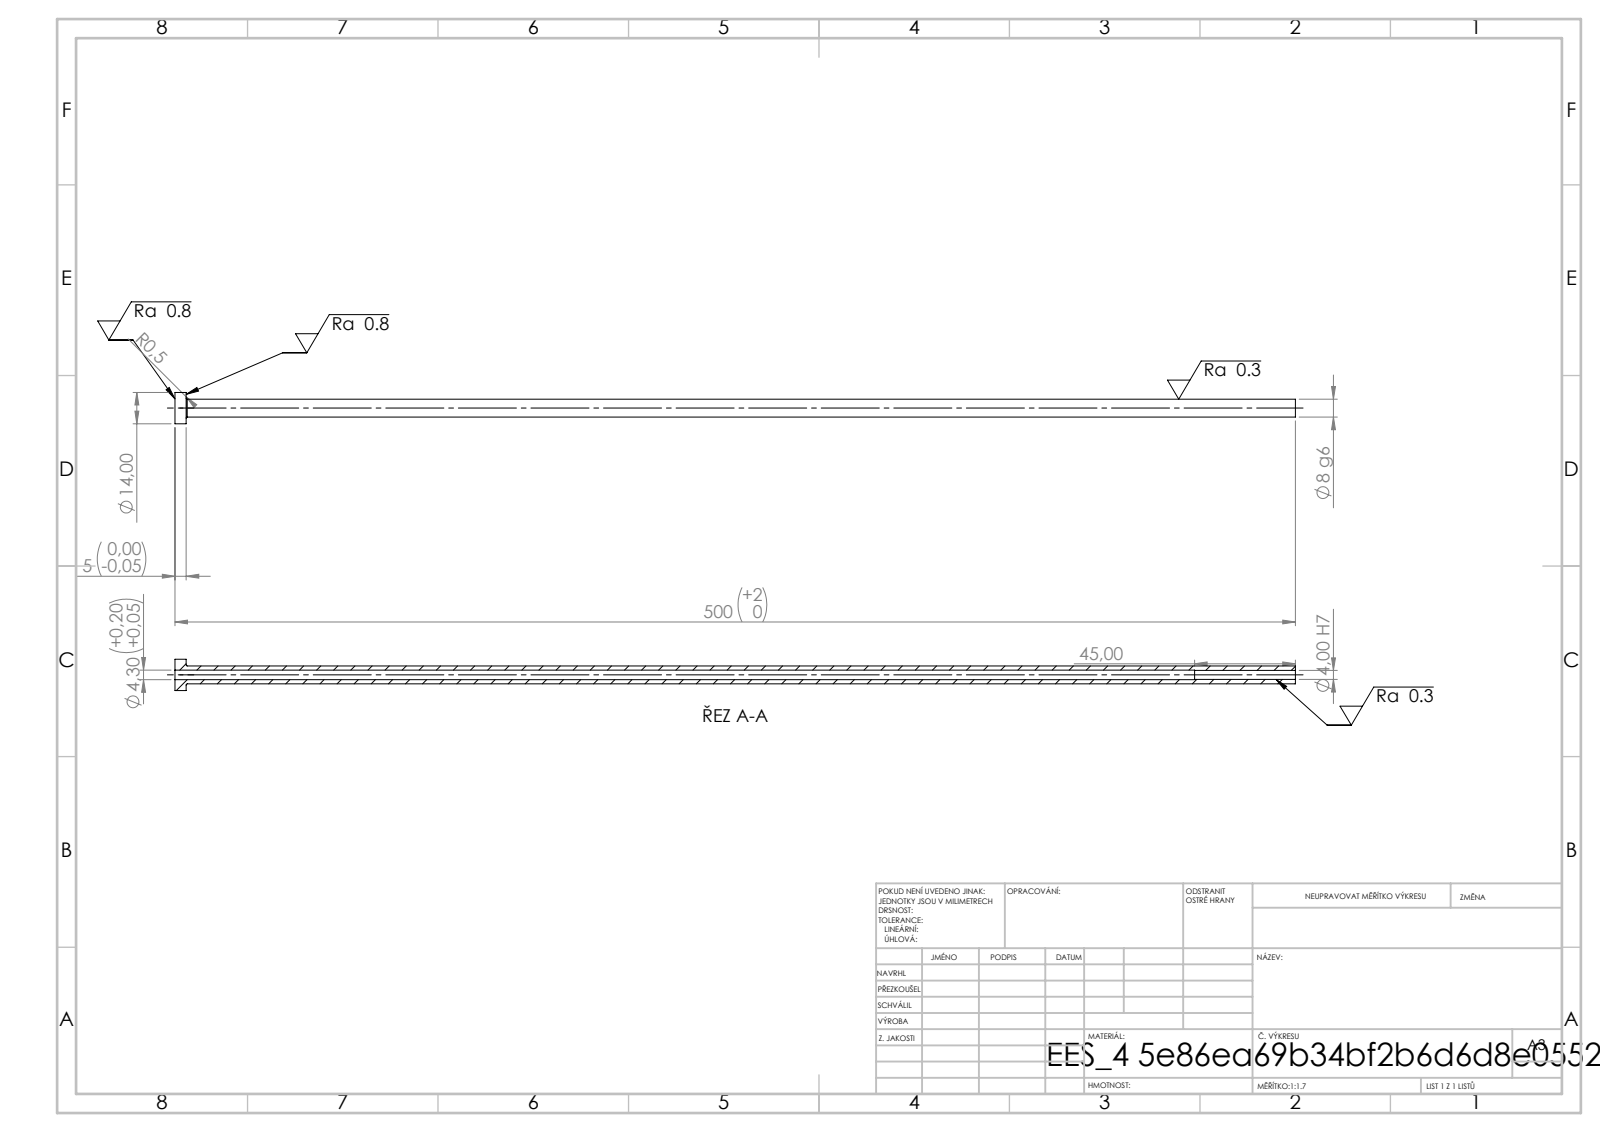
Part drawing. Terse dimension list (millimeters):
written by: SolidWorks 2019 (CONFIG_CONTROL_DESIGN)
unit: mm
bodies: 1 solid, 14 faces (4 planar, 8 cylindrical, 2 other)
size: 500 × 14 × 14
volume: 18 479 mm³; area: 19 650 mm²
holes: 1× ⌀4, 1× ⌀4.3
bosses: 1× ⌀14, 1× ⌀8
face distances: 5, 500, 495, 455, 450, 45
